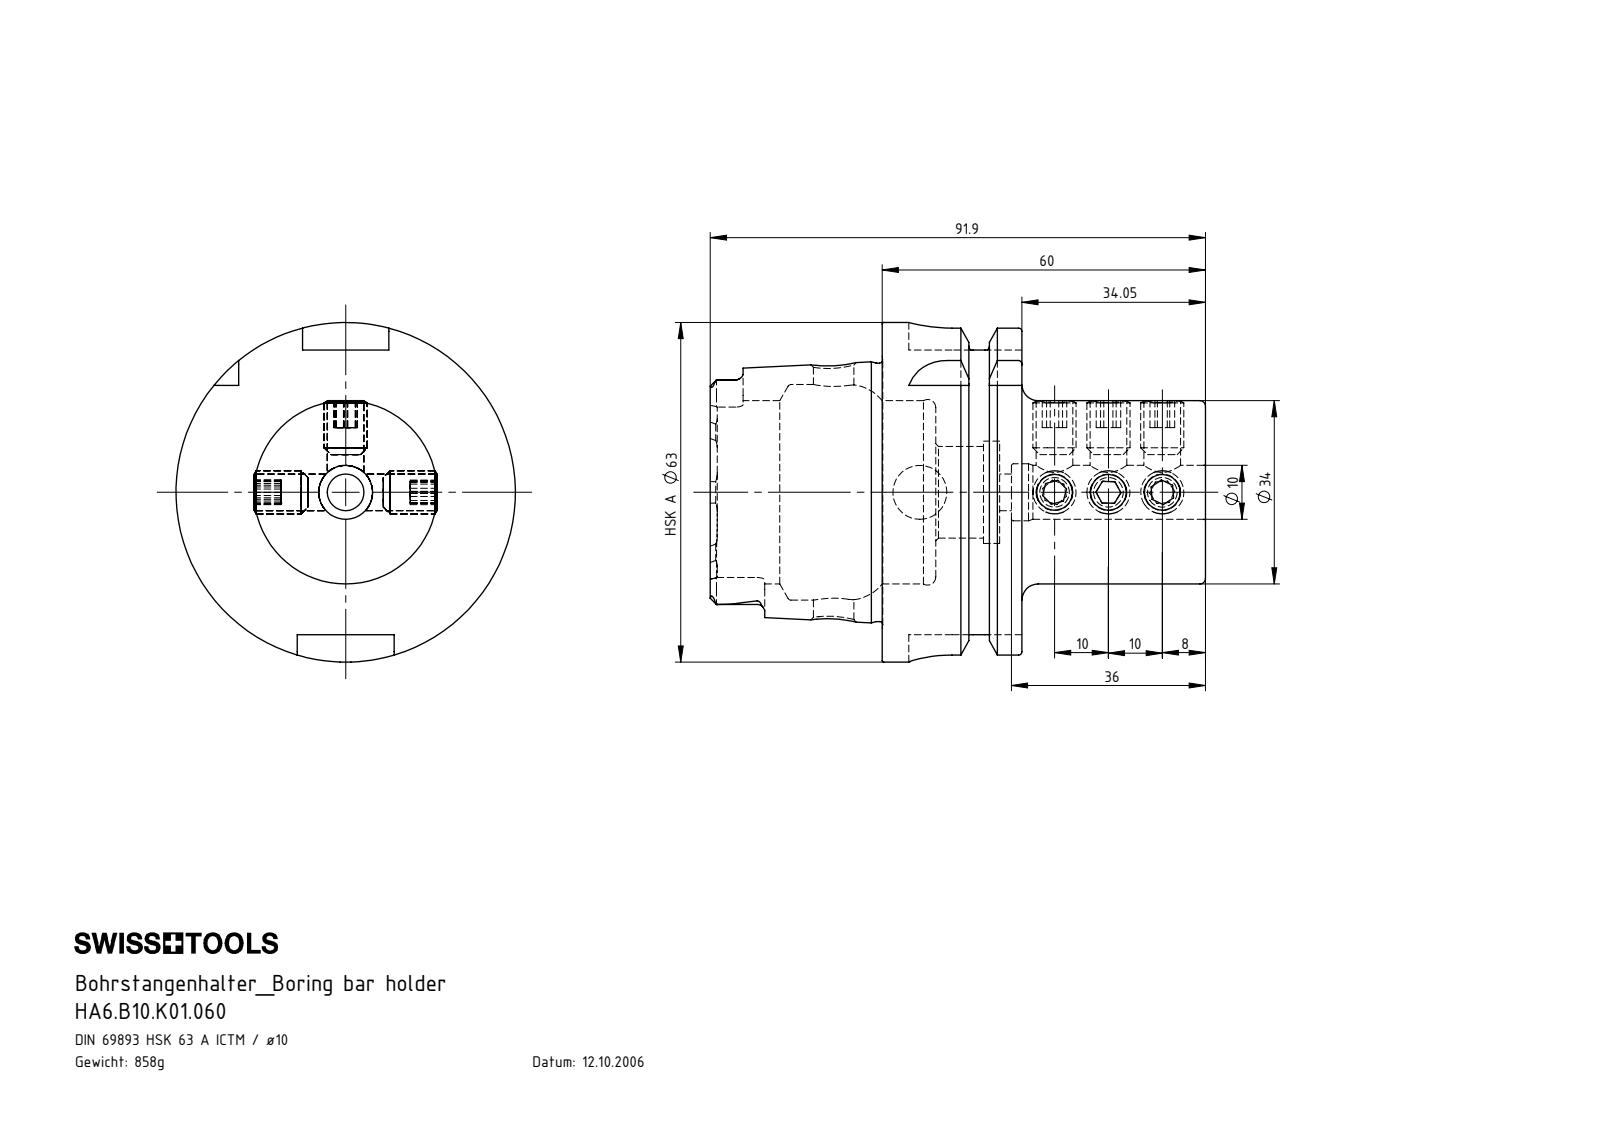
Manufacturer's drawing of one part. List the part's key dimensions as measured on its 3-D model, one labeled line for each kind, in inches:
Part name (STEP PRODUCT): ISO 4026 - M8 x 10; HA6-B10.K01.060_B_Fertigbearbeitung; HA6.B10.K01.060
STEP written by: SolidWorks 2017 (AUTOMOTIVE_DESIGN)
Units: inches
Bodies: 10 solids, 328 faces (128 planar, 85 cylindrical, 115 other)
Overall size (bounding box): 3.618 × 2.48 × 2.48
Volume: 6.672 in³ · Surface area: 49.65 in²
Round holes (diameter × count): ⌀0.268 ×7, ⌀0.394 ×2, ⌀0.295 ×1, ⌀0.417 ×1, ⌀0.669 ×1, ⌀0.748 ×1, ⌀1.339 ×1, ⌀1.575 ×1
Round bosses / shafts (diameter × count): ⌀0.315 ×6, ⌀2.48 ×1, ⌀2.163 ×1, ⌀1.887 ×1
Partial cylindrical surfaces — rounded edges, fillets, slot ends (radius × count): R0.055 ×6, R0.113 ×4, R0.315 ×4
Main face-to-face distances: 1.022, 2.362, 1.341, 0.63, 0.392, 1.97, 0.157, 1.256, 1.648, 2.278
Hole centre spacings: 0.394, 0.787, 0.984, 1.378, 1.614, 1.772, 2.008, 2.402
